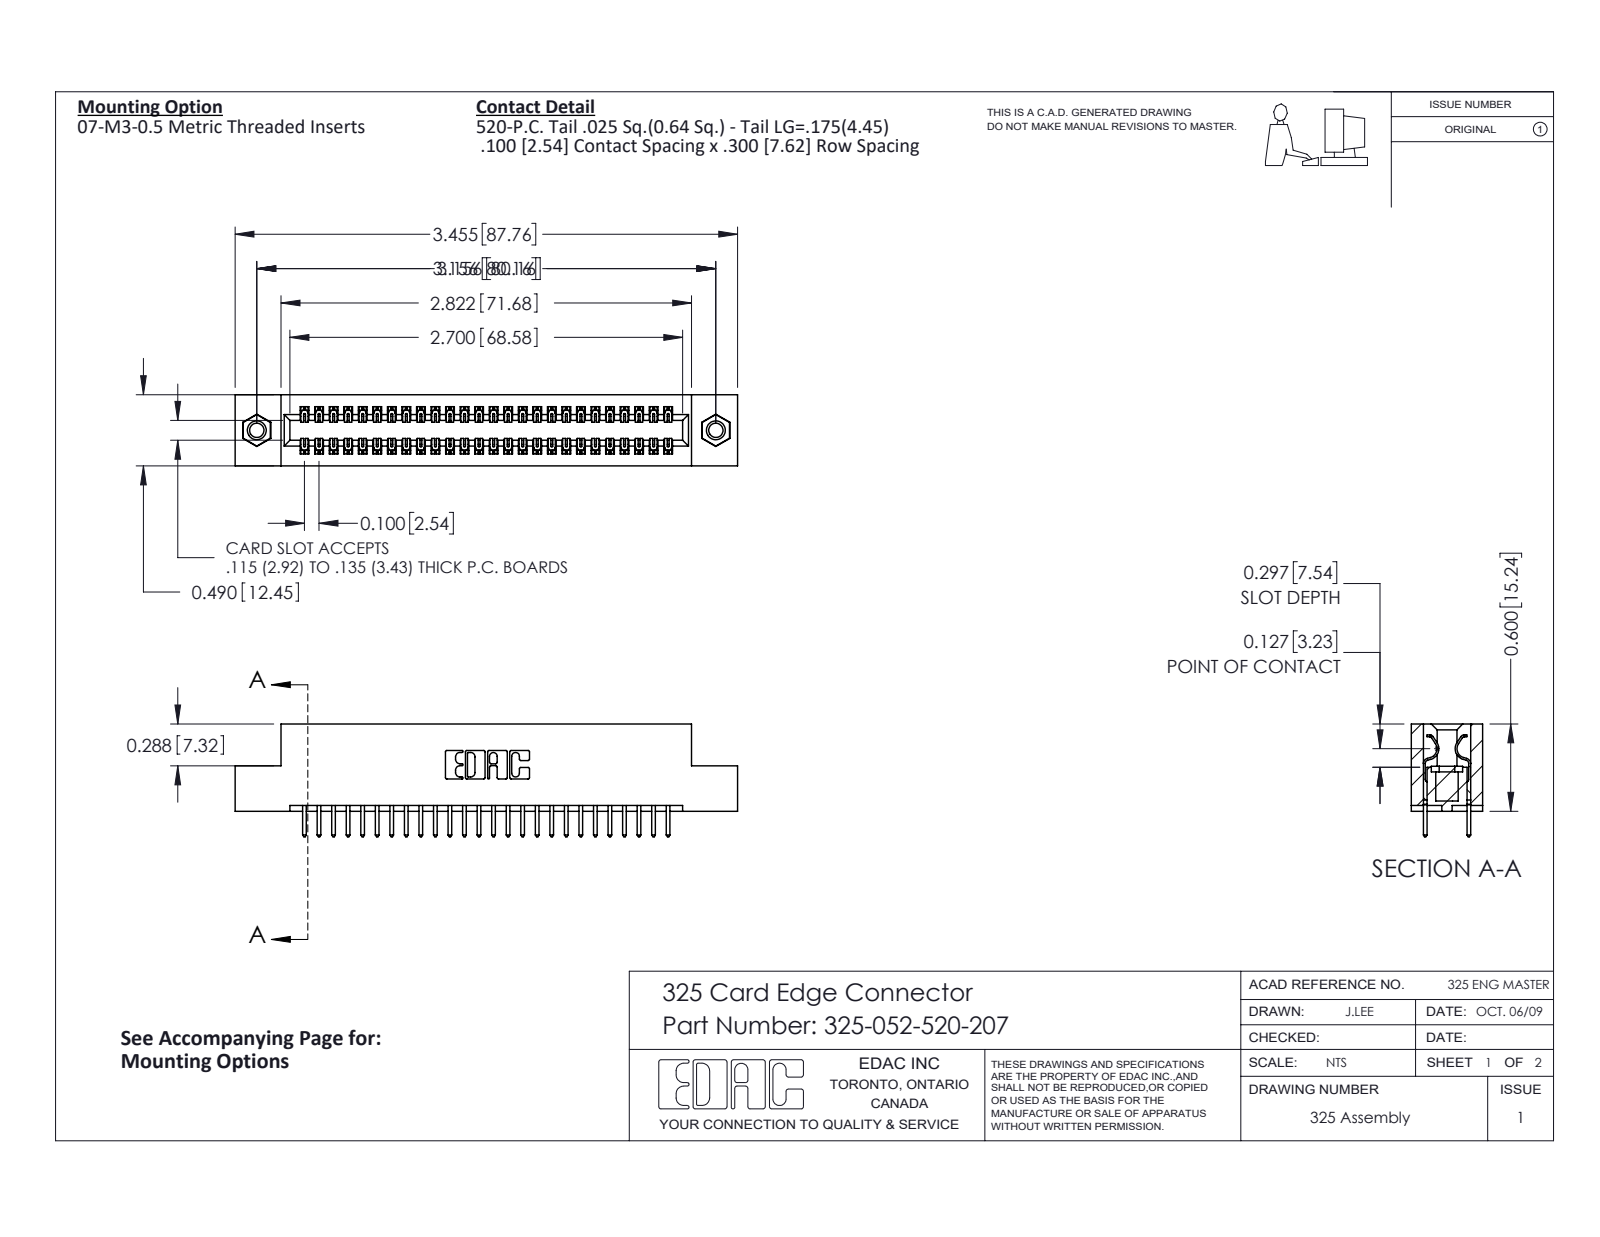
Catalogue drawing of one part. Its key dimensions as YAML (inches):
part_name: "325-052-520-207; 325-292-001_325-293-120; 345-250-001_345-250-005-103; 325 Part_TI"
step_written_by: "SolidWorks 2016 (CONFIG_CONTROL_DESIGN)"
units: inches
bodies: {solids: 55, faces: 2878, planar: 1974, cylindrical: 888, other: 16}
overall_size: [3.455, 0.775, 0.49]
volume: 0.681
surface_area: 20.23
round_holes:
  - {diameter: 0.098, count: 2}
  - {diameter: 0.125, count: 2}
  - {diameter: 0.16, count: 2}
round_bosses_or_shafts:
  - {diameter: 0.155, count: 2}
partial_cylinders:
  - {radius: 0.006, count: 78}
  - {radius: 0.01, count: 52}
  - {radius: 0.01, count: 22}
  - {radius: 0.007, count: 6}
  - {radius: 0.031, count: 6}
  - {radius: 0.026, count: 3}
  - {radius: 0.014, count: 2}
  - {radius: 0.022, count: 2}
face_to_face_distances: [0.083, 0.407, 0.3, 0.49, 0.107, 0.383, 0.025, 0.325, 0.04, 0.275]
hole_center_spacings: [3.156]
